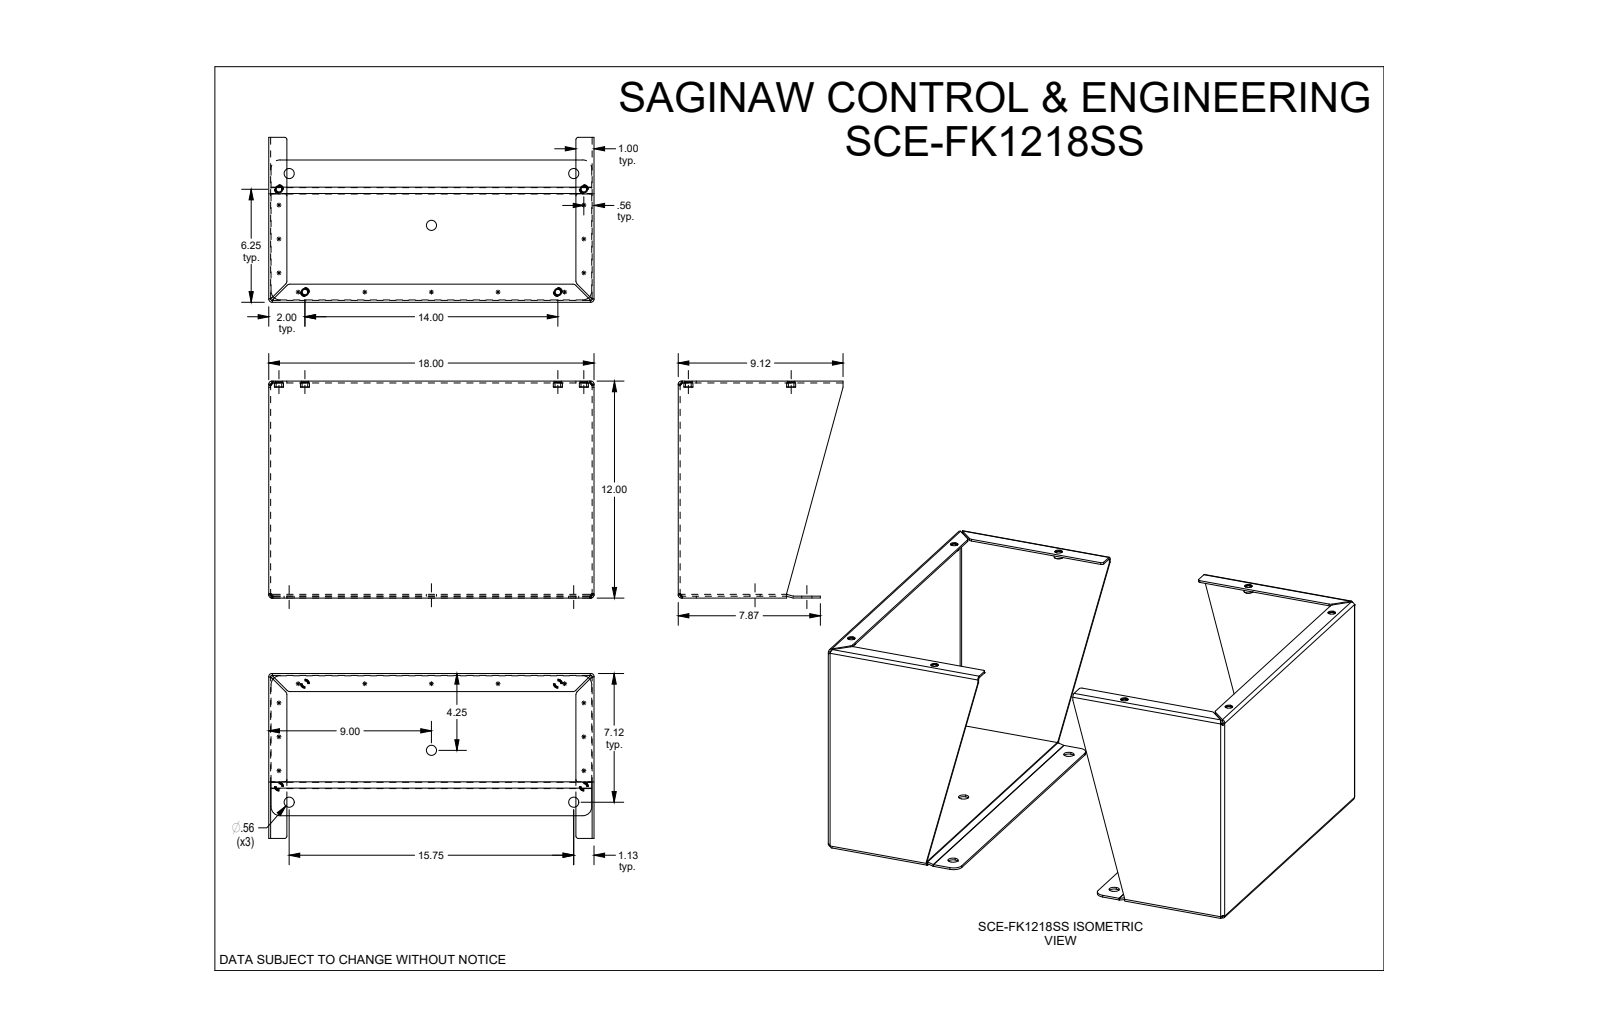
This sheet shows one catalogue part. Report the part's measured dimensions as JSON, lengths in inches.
{"part_name": "SCE-FK1218SS", "step_written_by": "SolidWorks 2019 (CONFIG_CONTROL_DESIGN)", "units": "inches", "bodies": {"solids": 12, "faces": 286, "planar": 120, "cylindrical": 110, "other": 56}, "overall_size": [24, 18, 12], "volume_in3": 121.2, "surface_area_in2": 2367, "round_holes": [[0.312, 8], [0.413, 8], [0.563, 6]], "round_bosses_or_shafts": [[0.5, 8], [0.412, 8]], "partial_cylinders_radius": [[0.166, 16], [0.062, 12], [0.125, 8], [0.22, 8], [0.5, 8], [0.063, 6]], "face_to_face_distances": [0.104, 23.896, 17.896, 23.792, 24, 18, 17.792, 11.792, 0.101, 11.893], "hole_center_spacings": [1.035, 5.866, 6.614, 7.913, 8.671, 10.646, 14.884, 15.919]}
